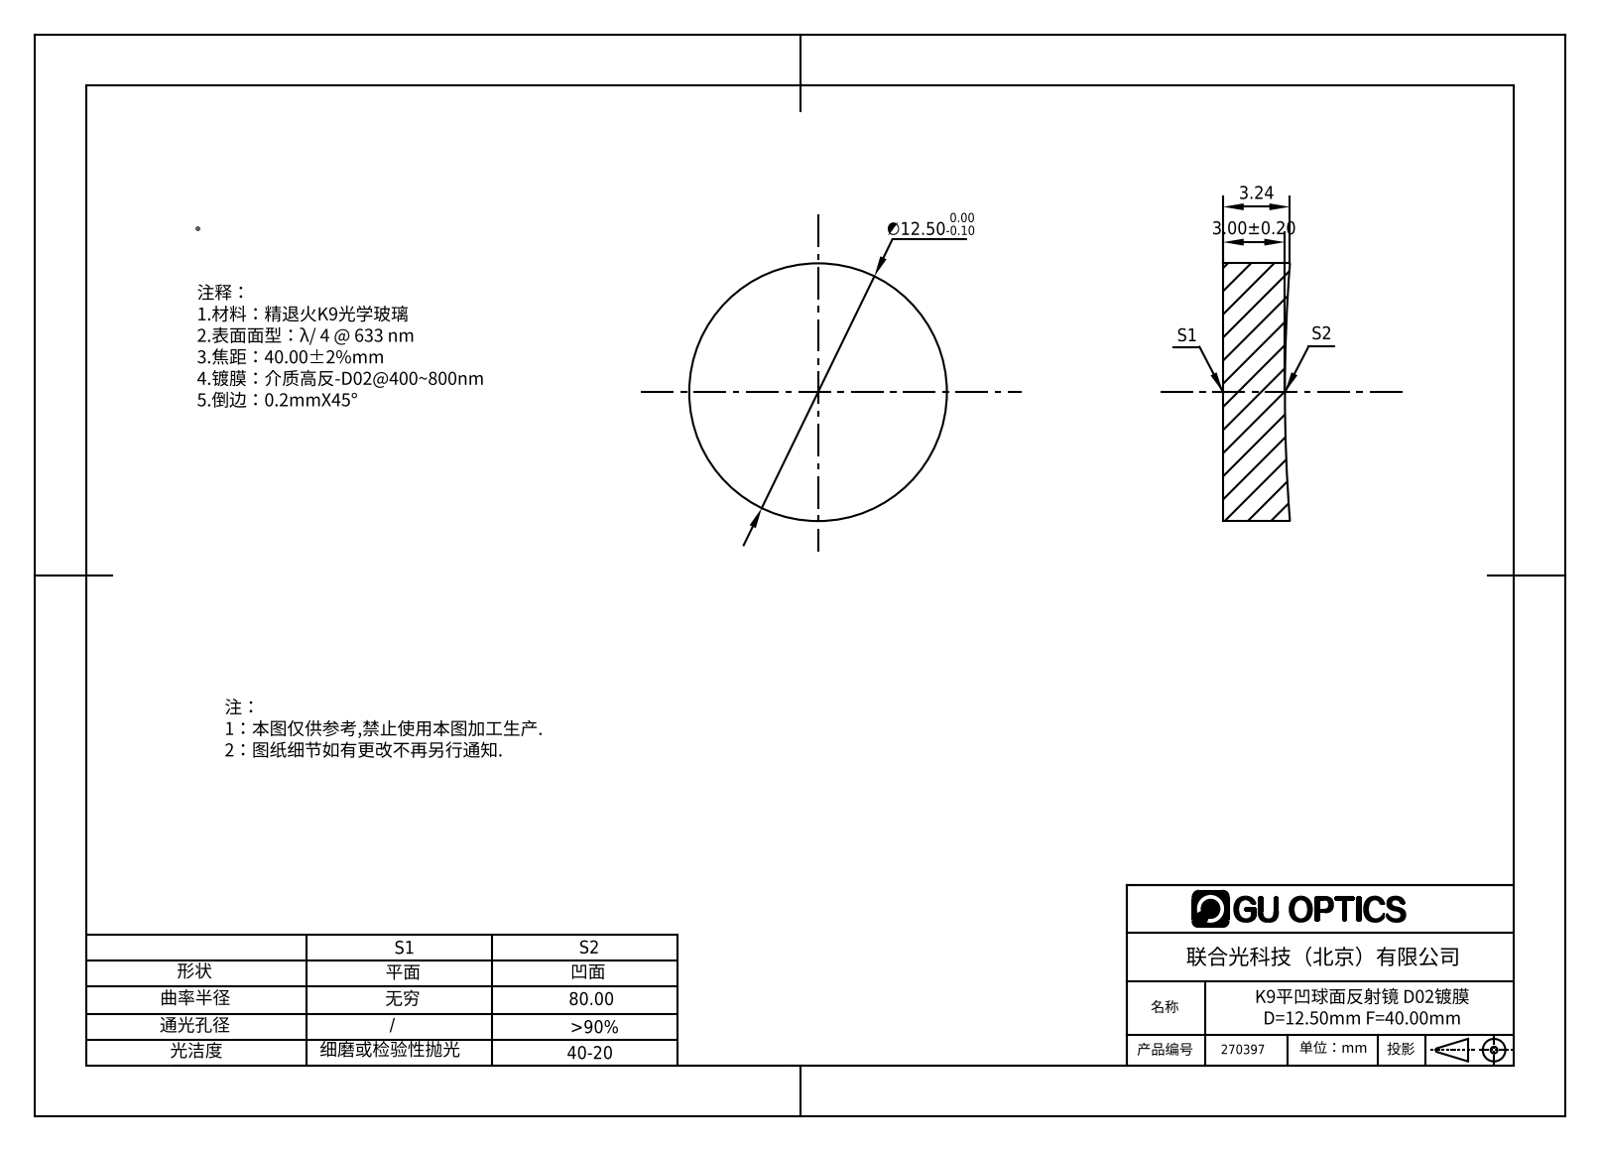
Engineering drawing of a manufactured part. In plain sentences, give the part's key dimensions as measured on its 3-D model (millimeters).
The part is named "270007". Its 3-D file was written by "SolidWorks 2016 (AUTOMOTIVE_DESIGN)". It is 1 solid with 5 faces: 1 planar, 2 cylindrical and 2 other. Overall it measures 12.5 by 12.5 by 3.25 millimeters. Its volume is 383 cubic millimeters and its surface area 373 square millimeters. Round bosses or shafts: 1 of diameter 12.5.
